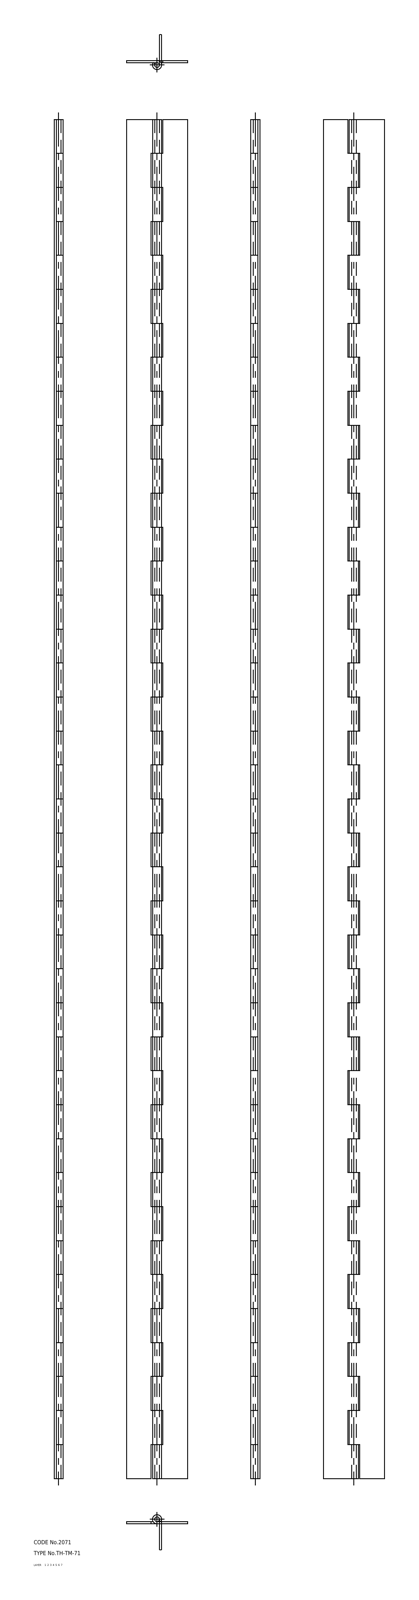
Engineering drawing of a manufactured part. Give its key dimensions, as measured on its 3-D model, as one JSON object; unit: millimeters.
{"part_name": "hinge piece_B; hinge piece_A; shaft; TH_TM_71_25187_36", "step_written_by": "CADfix (AUTOMOTIVE_DESIGN)", "units": "millimeters", "bodies": {"solids": 3, "faces": 252, "planar": 0, "cylindrical": 0, "other": 252}, "overall_size": [1000, 45, 6.7], "volume_mm3": 96158, "surface_area_mm2": 127953}
